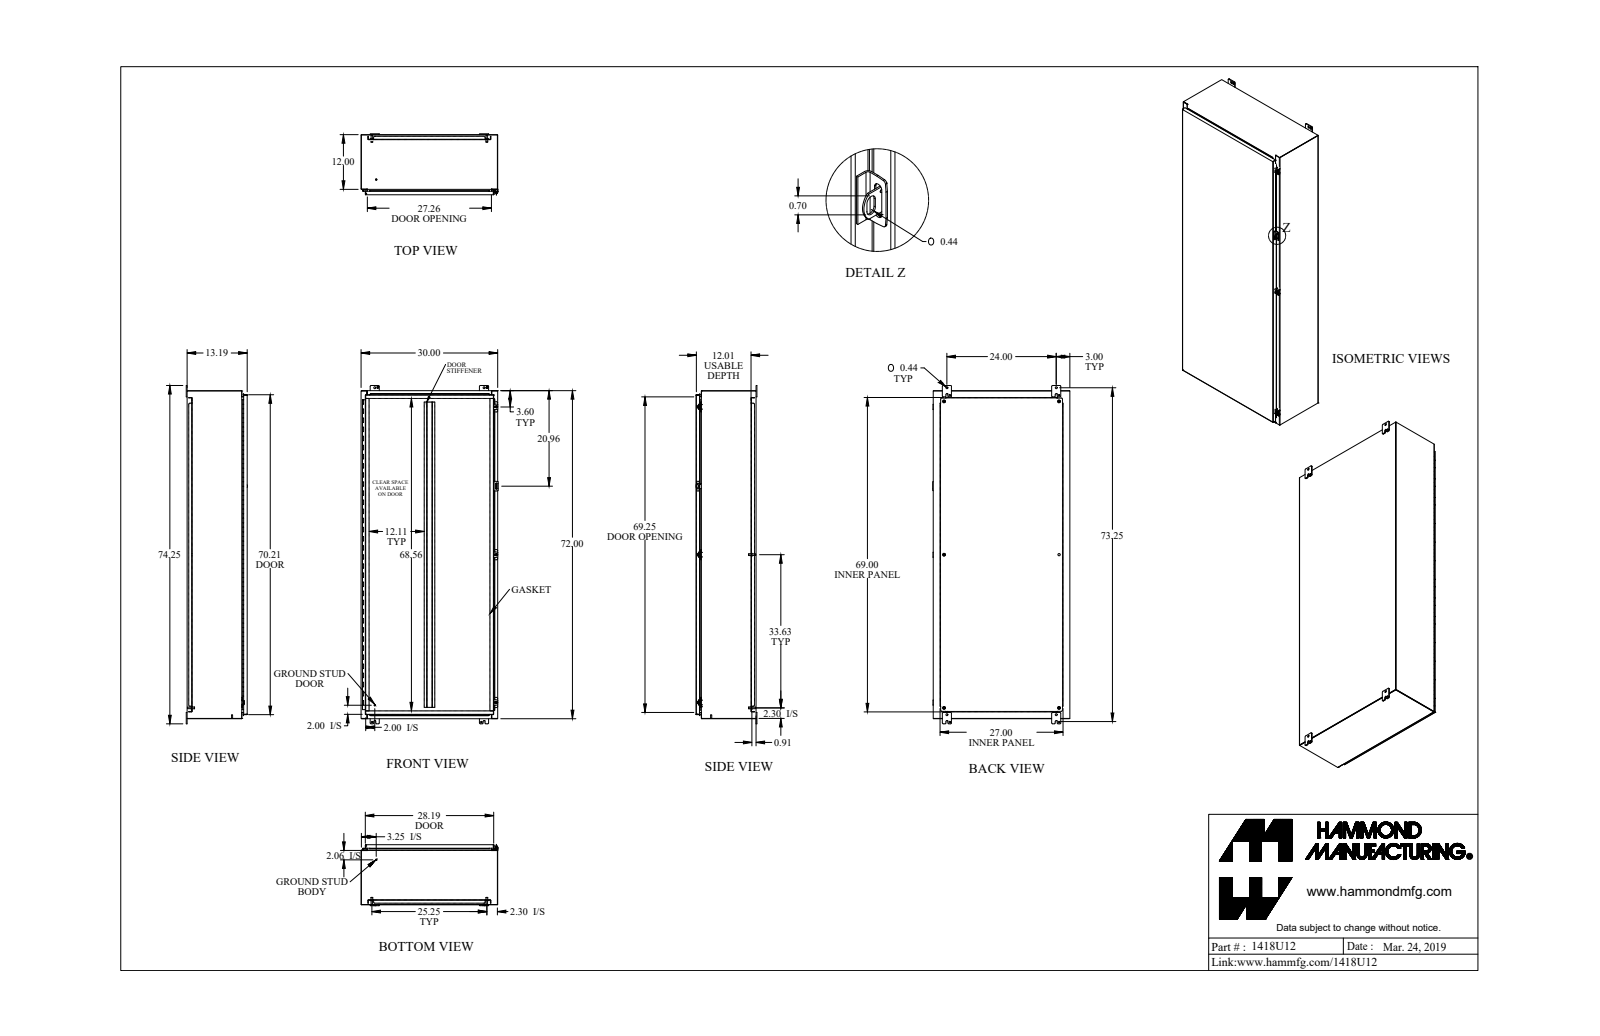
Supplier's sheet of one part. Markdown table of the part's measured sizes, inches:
| quantity | value |
| --- | --- |
| part name | 1418U12_Default |
| STEP written by | SolidWorks 2019 (CONFIG_CONTROL_DESIGN) |
| units | inches |
| bodies | 50 solids, 1846 faces (1008 planar, 778 cylindrical, 60 other) |
| overall size | 74.25 × 30.128 × 13.437 |
| volume | 781.8 in³ |
| surface area | 20 164 in² |
| round holes (diameter × count) | 0.304 × 12, 0.5 × 6, 0.307 × 4, 0.313 × 4, 0.437 × 4, 0.445 × 4, 0.213 × 3, 0.265 × 3, 0.375 × 3, 0.11 × 1, 0.125 × 1 |
| round bosses / shafts (diameter × count) | 0.65 × 6, 0.375 × 6, 0.33 × 6, 1 × 4, 0.5 × 3, 0.39 × 3, 0.244 × 3, 0.281 × 2 |
| partial cylindrical surfaces (radius × count) | 0.188 × 38, 0.036 × 22, 0.108 × 22, 0.25 × 20, 0.048 × 19, 0.143 × 19, 0.116 × 16, 0.125 × 8 |
| main face-to-face distances | 0.072, 13.113, 13.041, 13.185, 0.095, 12.081, 12.009, 1.032, 1.104, 12.176 |
| hole center spacings | 24, 6, 12, 18, 30, 36, 33.625, 42 |
